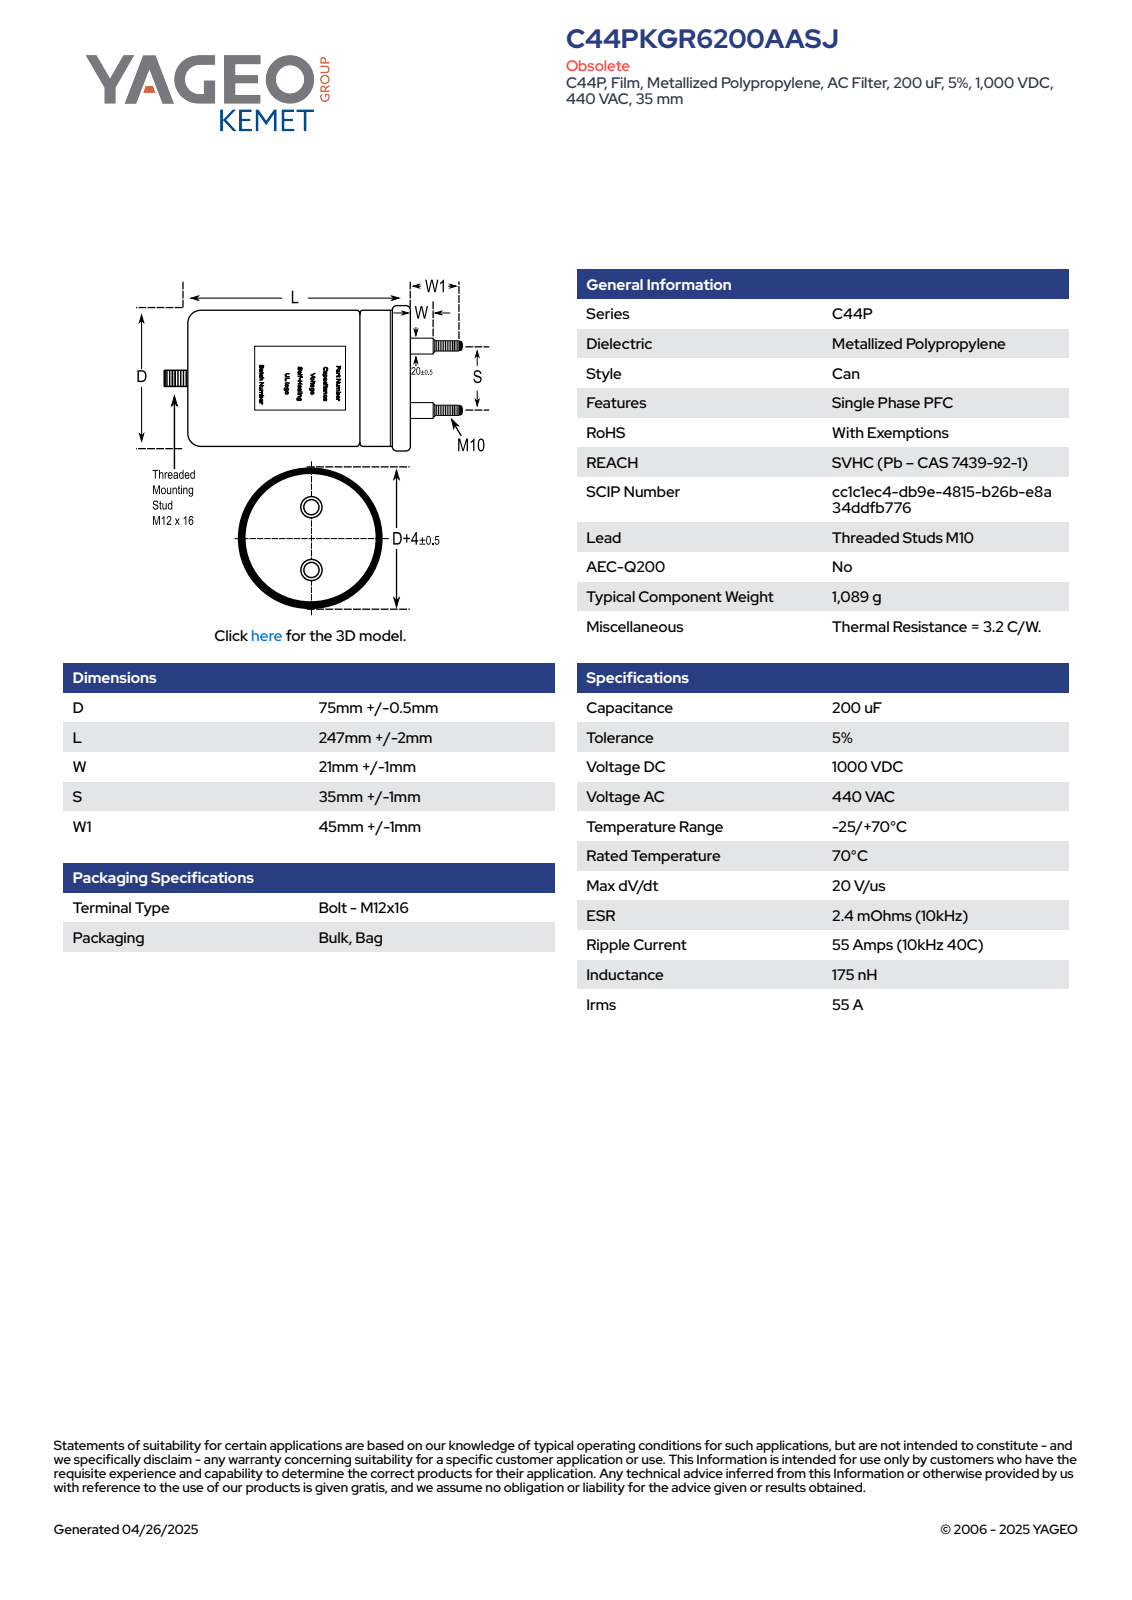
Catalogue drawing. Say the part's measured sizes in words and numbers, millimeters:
The part is named "CFP_C44P_75X247_D75.5L249S35". Its 3-D file was written by "SolidWorks 2014 (AUTOMOTIVE_DESIGN)". It is 1 solid with 105 faces: 32 planar, 36 cylindrical and 37 other. Overall it measures 311 by 80 by 80 millimeters. Its volume is 1 137 000 cubic millimeters and its surface area 73 384 square millimeters. Round bosses or shafts: 3 of diameter 12, 2 of diameter 20.5, 2 of diameter 10, 1 of diameter 80, 1 of diameter 75.5. Partial cylindrical surfaces (rounded edges, fillets, slot ends): 1 of radius 37.76. The main face-to-face distances are 249, 270, 21, 241.01, 7.99, 28.99, 295, 53.99, 46, 25.
